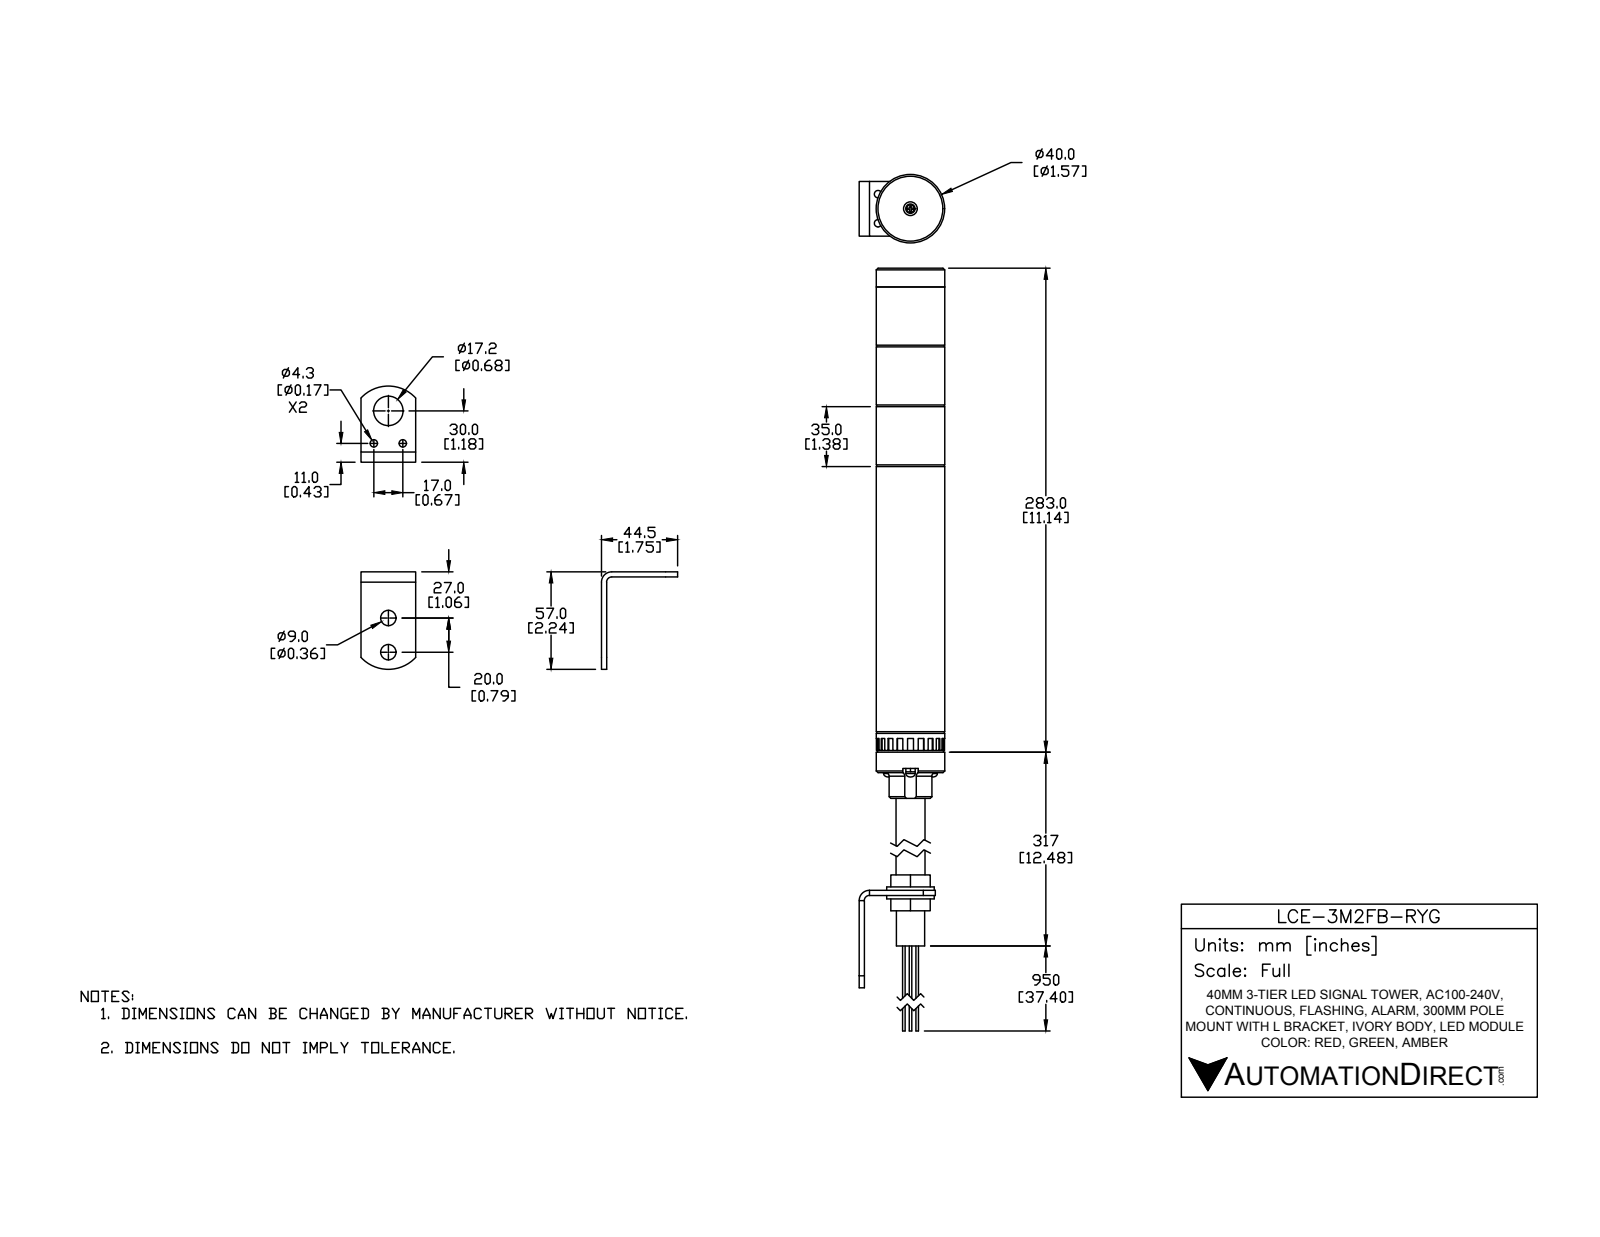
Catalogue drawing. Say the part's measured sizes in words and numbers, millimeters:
The part is named "LCE-3M2FB-RYG". Its 3-D file was written by "SolidWorks 2016 (AUTOMOTIVE_DESIGN)". It is 38 solids with 397 faces: 251 planar, 126 cylindrical and 20 other. Overall it measures 701 by 50 by 40 millimeters. Its volume is 432 518 cubic millimeters and its surface area 141 262 square millimeters. Round holes: 3 of diameter 3.5, 3 of diameter 4, 2 of diameter 4.3, 2 of diameter 9.04, 1 of diameter 8, 1 of diameter 12, 1 of diameter 17.2, 1 of diameter 17.5, 1 of diameter 18. Round bosses or shafts: 10 of diameter 1.5, 6 of diameter 3, 4 of diameter 5.5, 1 of diameter 40, 1 of diameter 39.5, 1 of diameter 38.5, 1 of diameter 27.8, 1 of diameter 17. Partial cylindrical surfaces (rounded edges, fillets, slot ends): 3 of radius 4.5, 2 of radius 21.79, 1 of radius 3, 1 of radius 6, 1 of radius 12.5. The main face-to-face distances are 35, 1, 70, 34, 11, 36, 69, 156, 191, 226. The hole center spacings are 15, 25.98, 20.81, 6.09, 17, 17.09, 20, 20.08.
